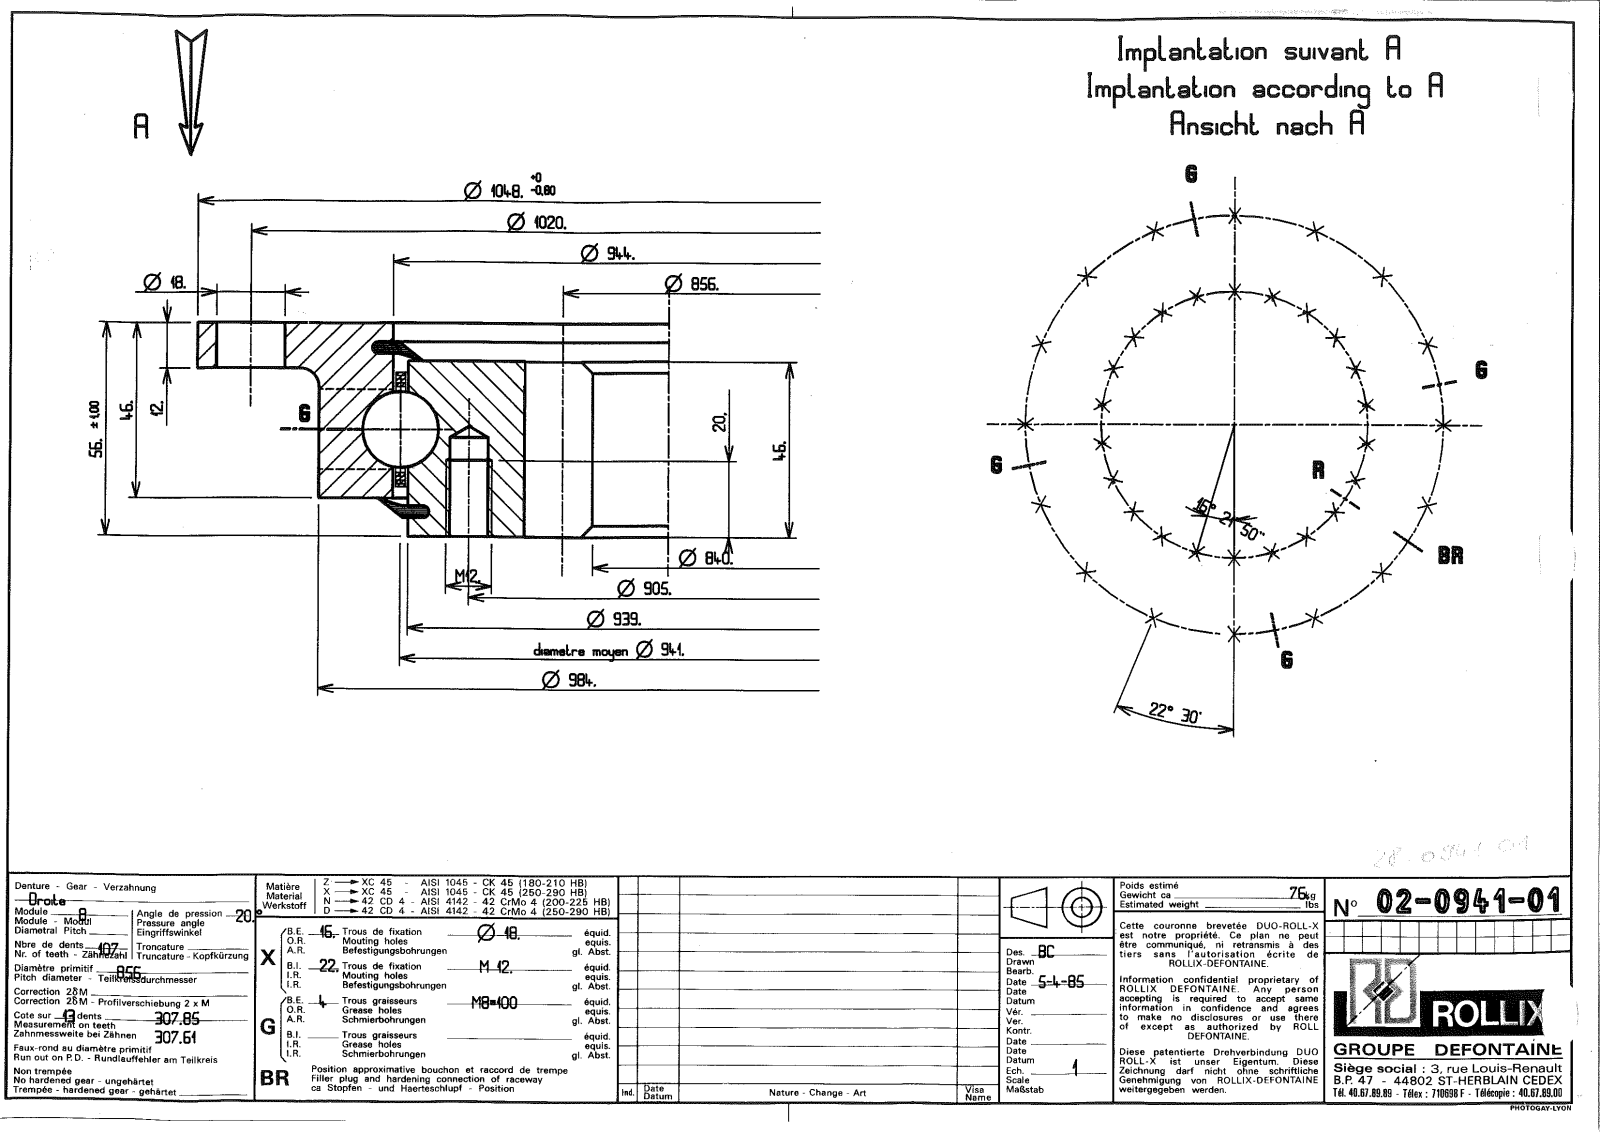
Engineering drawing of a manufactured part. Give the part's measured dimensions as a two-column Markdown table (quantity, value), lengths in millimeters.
| quantity | value |
| --- | --- |
| part name | 22-0941-01 |
| STEP written by | SolidWorks 2016 (CONFIG_CONTROL_DESIGN) |
| units | millimeters |
| bodies | 9 solids, 919 faces (267 planar, 323 cylindrical, 329 other) |
| overall size | 1048 × 1048 × 56 |
| volume | 8 435 000 mm³ |
| surface area | 1 493 000 mm² |
| round holes (diameter × count) | 10.25 × 22, 18 × 16, 7 × 4, 945.5 × 1 |
| round bosses / shafts (diameter × count) | 8 × 4, 1048 × 1, 984 × 1, 936.5 × 1 |
| partial cylindrical surfaces (radius × count) | 420 × 1, 438 × 1 |
| main face-to-face distances | 10, 46, 56, 44, 2, 12, 34, 36, 4.95, 51.05 |
| hole center spacings | 489.28, 895.79, 868.34, 375.95, 128.8, 823.22, 254.97, 683.95 |
